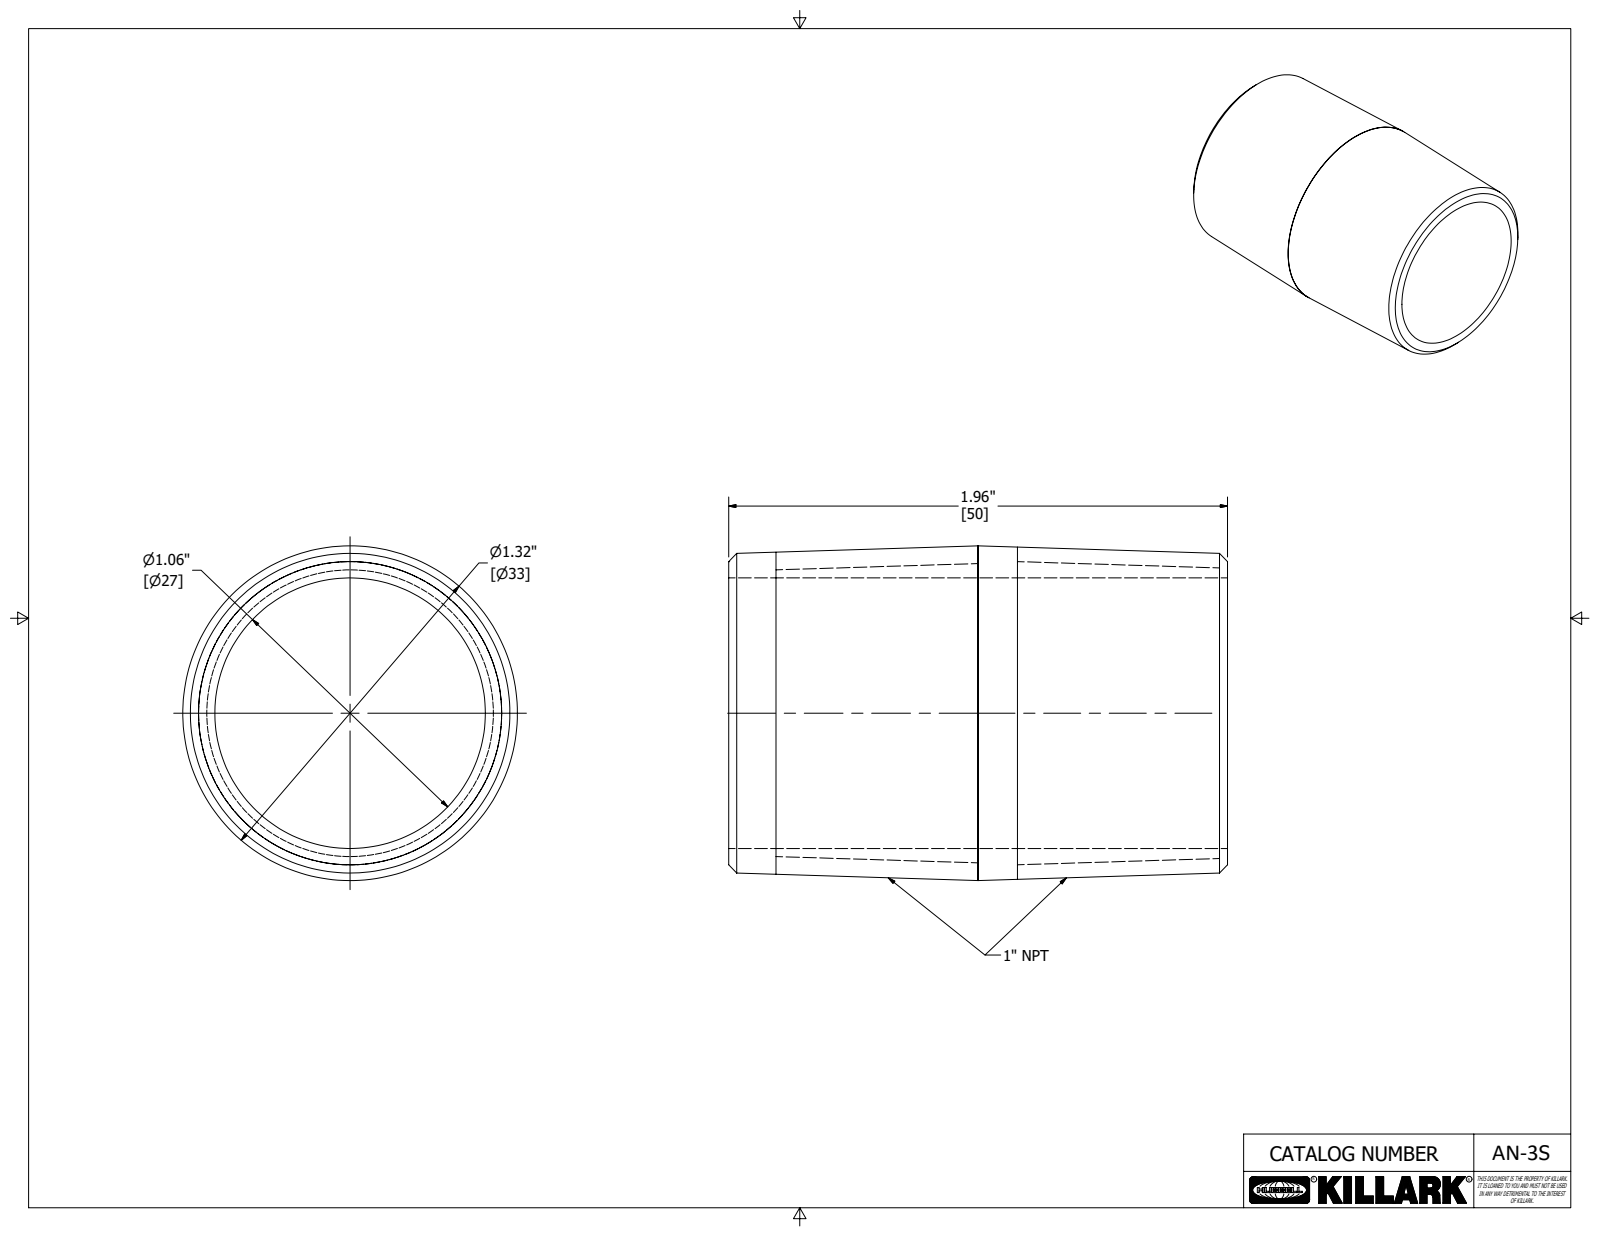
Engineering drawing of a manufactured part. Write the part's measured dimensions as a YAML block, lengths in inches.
part_name: "14077-3"
step_written_by: "Autodesk Inventor 2020 (AUTOMOTIVE_DESIGN)"
units: inches
bodies: {solids: 1, faces: 8, planar: 2, cylindrical: 2, other: 4}
overall_size: [1.96, 1.315, 1.315]
volume: 0.797
surface_area: 15.01
round_holes:
  - {diameter: 1.063, count: 1}
round_bosses_or_shafts:
  - {diameter: 1.315, count: 1}
face_to_face_distances: [1.96]
